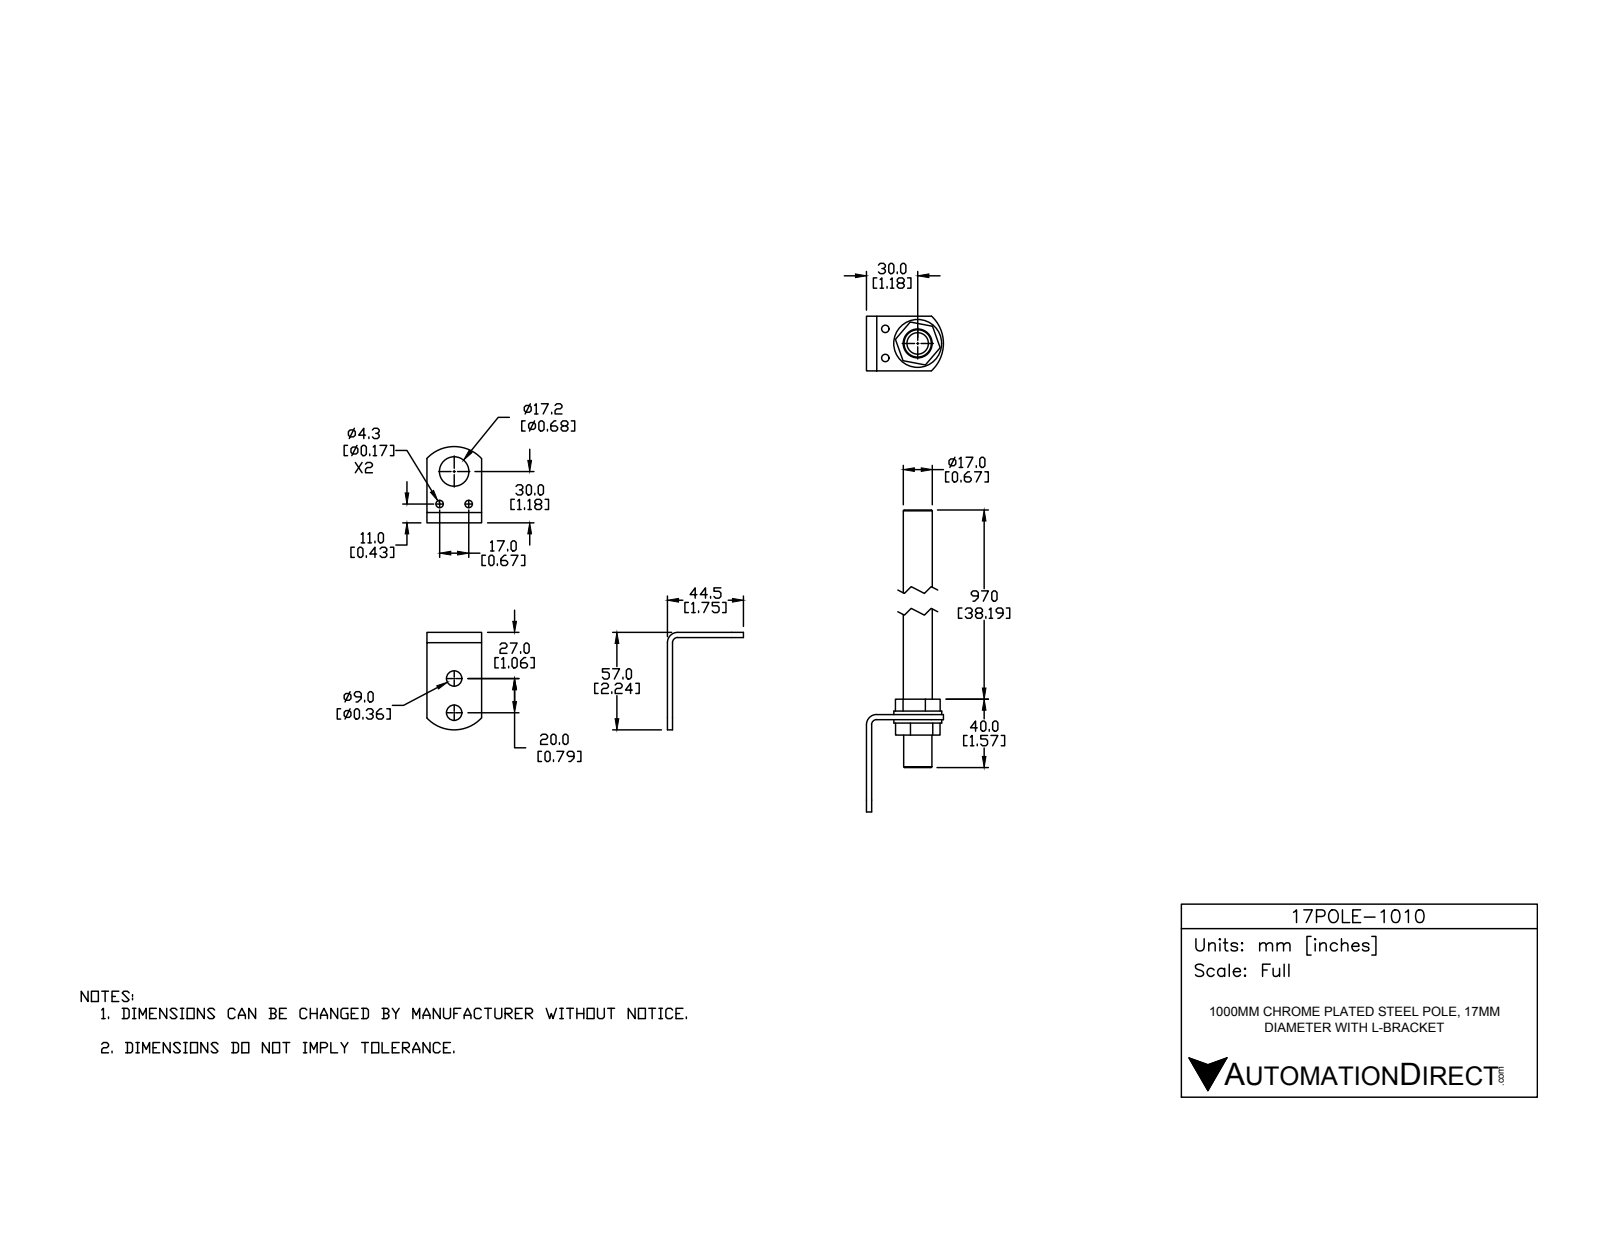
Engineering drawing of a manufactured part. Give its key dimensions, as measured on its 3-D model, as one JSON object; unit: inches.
{"part_name": "17POLE-1010-WASHER; 17POLE-1010; SZ-012; 17POLE-1010-POLE (+1 more)", "step_written_by": "SolidWorks 2016 (AUTOMOTIVE_DESIGN)", "units": "inches", "bodies": {"solids": 6, "faces": 69, "planar": 33, "cylindrical": 32, "other": 4}, "overall_size": [40.787, 1.772, 1.26], "volume_in3": 7.044, "surface_area_in2": 163.1, "round_holes": [[0.169, 2], [0.356, 2], [0.496, 1], [0.65, 1], [0.677, 1], [0.689, 1]], "round_bosses_or_shafts": [[1.102, 1], [0.669, 1]], "partial_cylinders_radius": [[0.858, 2], [0.118, 1], [0.236, 1]], "face_to_face_distances": [0.118, 0.079, 0.197, 0.276, 0.354, 0.472, 0.551, 0.906, 1.26, 0.827], "hole_center_spacings": [0.819, 0.669, 0.787]}
